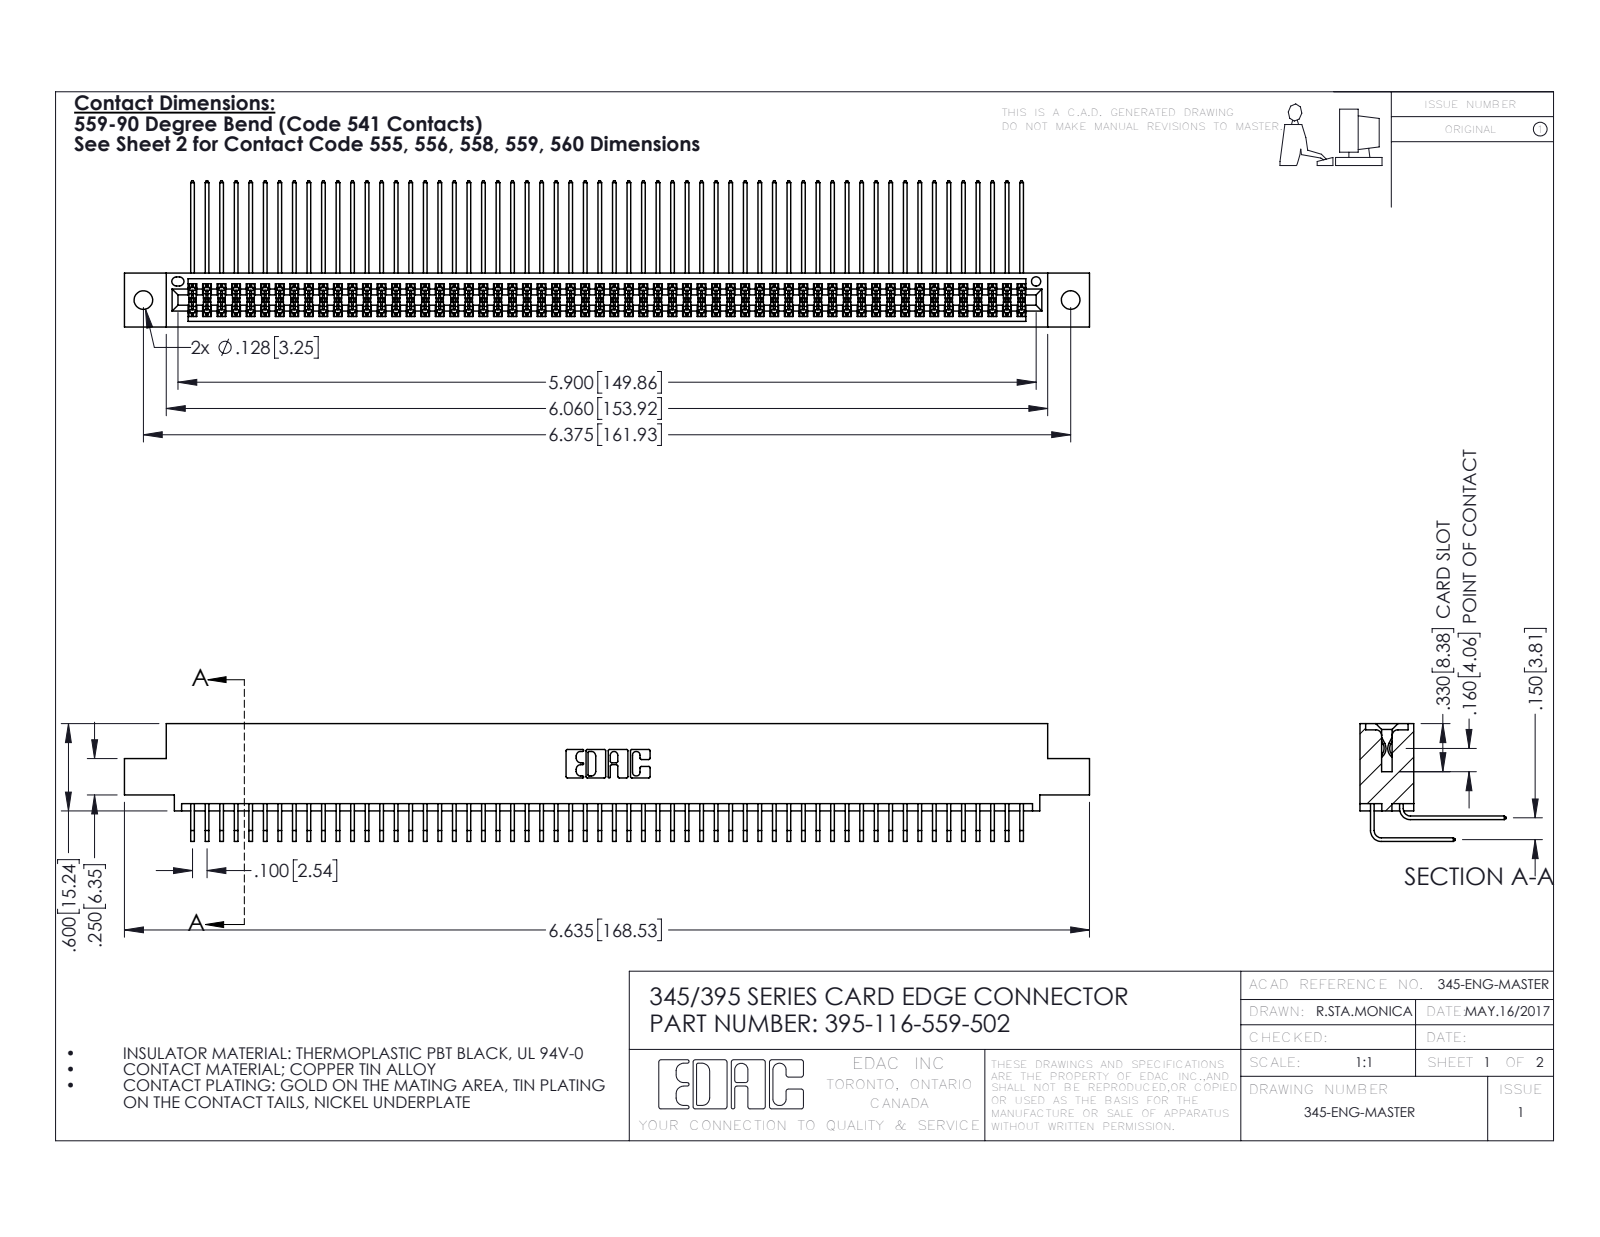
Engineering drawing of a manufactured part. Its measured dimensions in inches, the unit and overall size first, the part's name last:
Units: inches
Overall size (bounding box): 6.635 × 1.005 × 0.809
Round holes (diameter × count): ⌀0.128 ×2, ⌀0.064 ×1
Partial cylindrical surfaces — rounded edges, fillets, slot ends (radius × count): R0.006 ×174, R0.01 ×22, R0.007 ×6, R0.031 ×6, R0.026 ×3, R0.014 ×2, R0.019 ×2, R0.022 ×2
Main face-to-face distances: 0.072, 0.298, 0.2, 0.37, 0.098, 0.272, 0.025, 0.225, 0.175, 0.15
Hole centre spacings: 0.27, 6.139, 6.375
Volume: 1.042 in³ · Surface area: 44.21 in²
Bodies: 117 solids, 6162 faces (4144 planar, 2018 cylindrical, 0 other)
Part name (STEP PRODUCT): 345-292-001_558 559 Tail - 1; 395-116-559-502; 345 Part_0.110 Offset - 0.128 Dia; 345-292-001_559 Tail - 2
STEP written by: SolidWorks 2016 (CONFIG_CONTROL_DESIGN)
